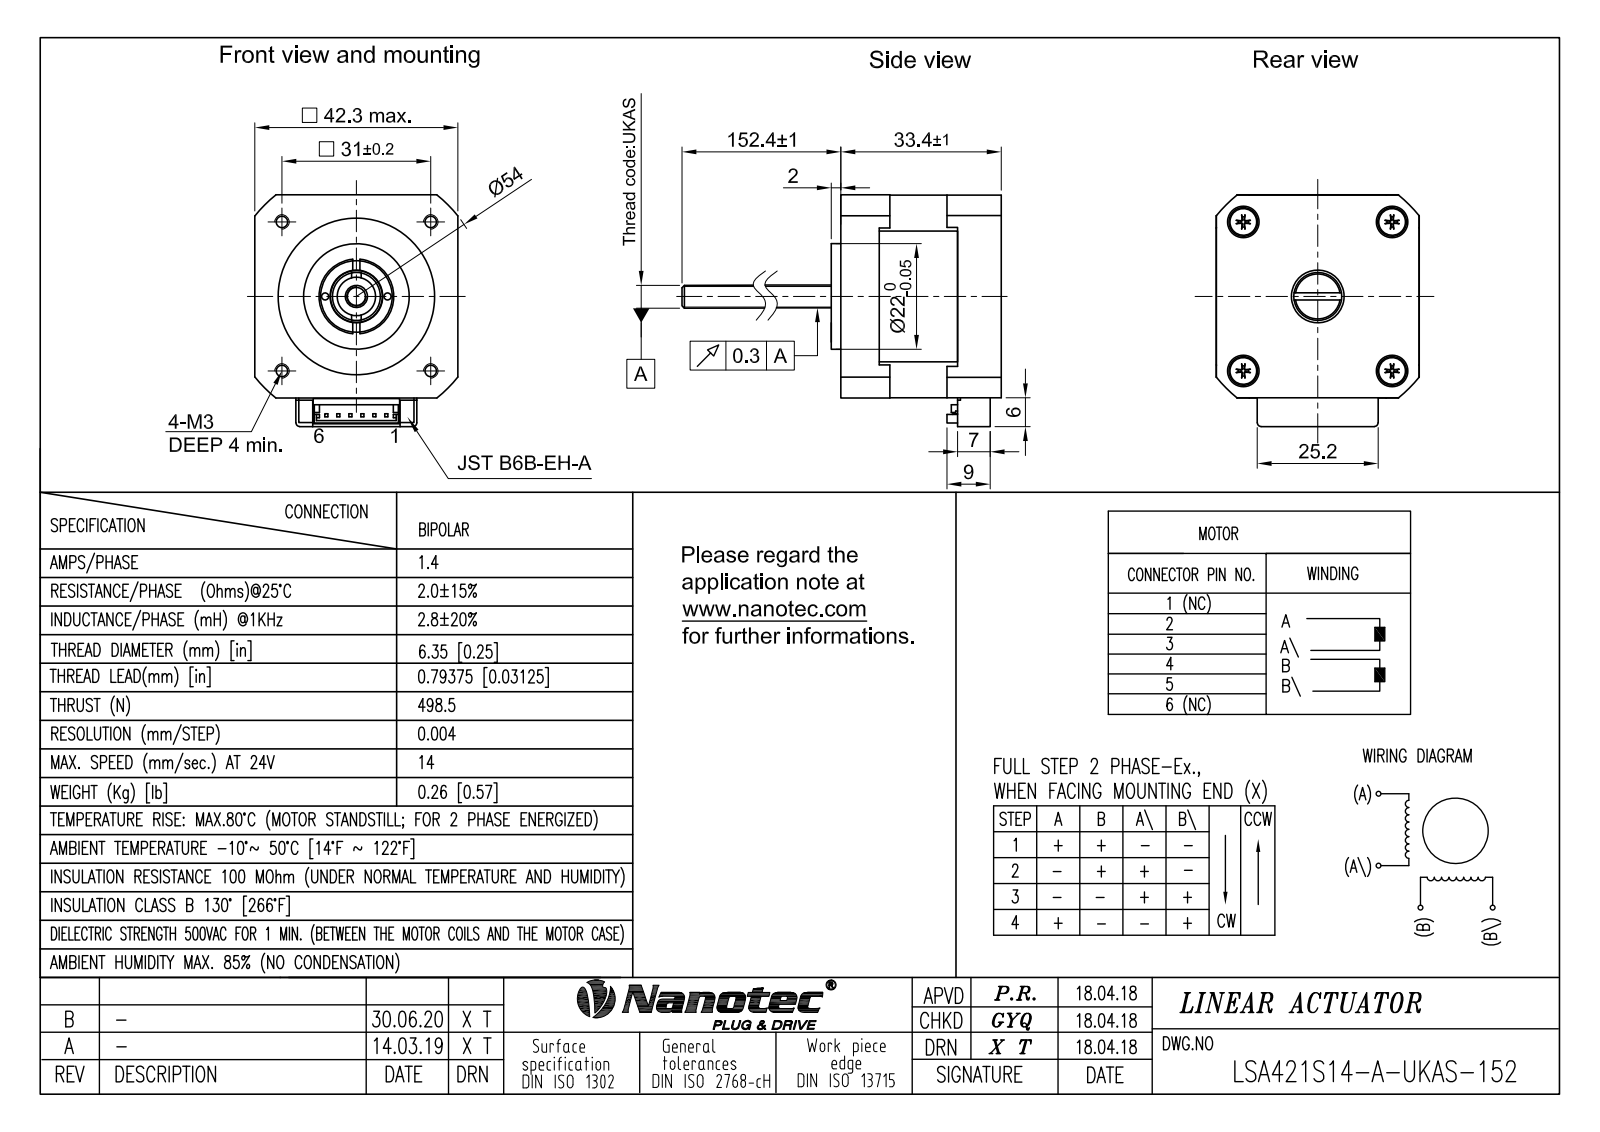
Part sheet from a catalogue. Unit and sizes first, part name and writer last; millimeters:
Units: millimetres
Overall size (bounding box): 185.4 × 48.3 × 42.3
Round holes (diameter × count): ⌀2.5 ×4, ⌀3.4 ×4, ⌀6 ×4, ⌀10 ×1, ⌀11 ×1, ⌀32.6 ×1
Round bosses / shafts (diameter × count): ⌀3 ×4, ⌀2.67 ×4, ⌀22 ×1, ⌀6.35 ×1
Partial cylindrical surfaces — rounded edges, fillets, slot ends (radius × count): R0.2 ×8, R0.8 ×8, R0.6 ×6, R15.2 ×1, R25.11 ×1, R25.5 ×1, R27 ×1
Main face-to-face distances: 42.25, 42.3, 33.4, 42.2, 0.5, 0.6, 32.9, 2, 2.5, 35.4
Hole centre spacings: 21.92, 31, 43.84
Volume: 62 379 mm³ · Surface area: 16 041 mm²
Bodies: 2 solids, 441 faces (280 planar, 75 cylindrical, 86 other)
Part name (STEP PRODUCT): 零件22
STEP written by: Autodesk Inventor 2013 (CONFIG_CONTROL_DESIGN)
